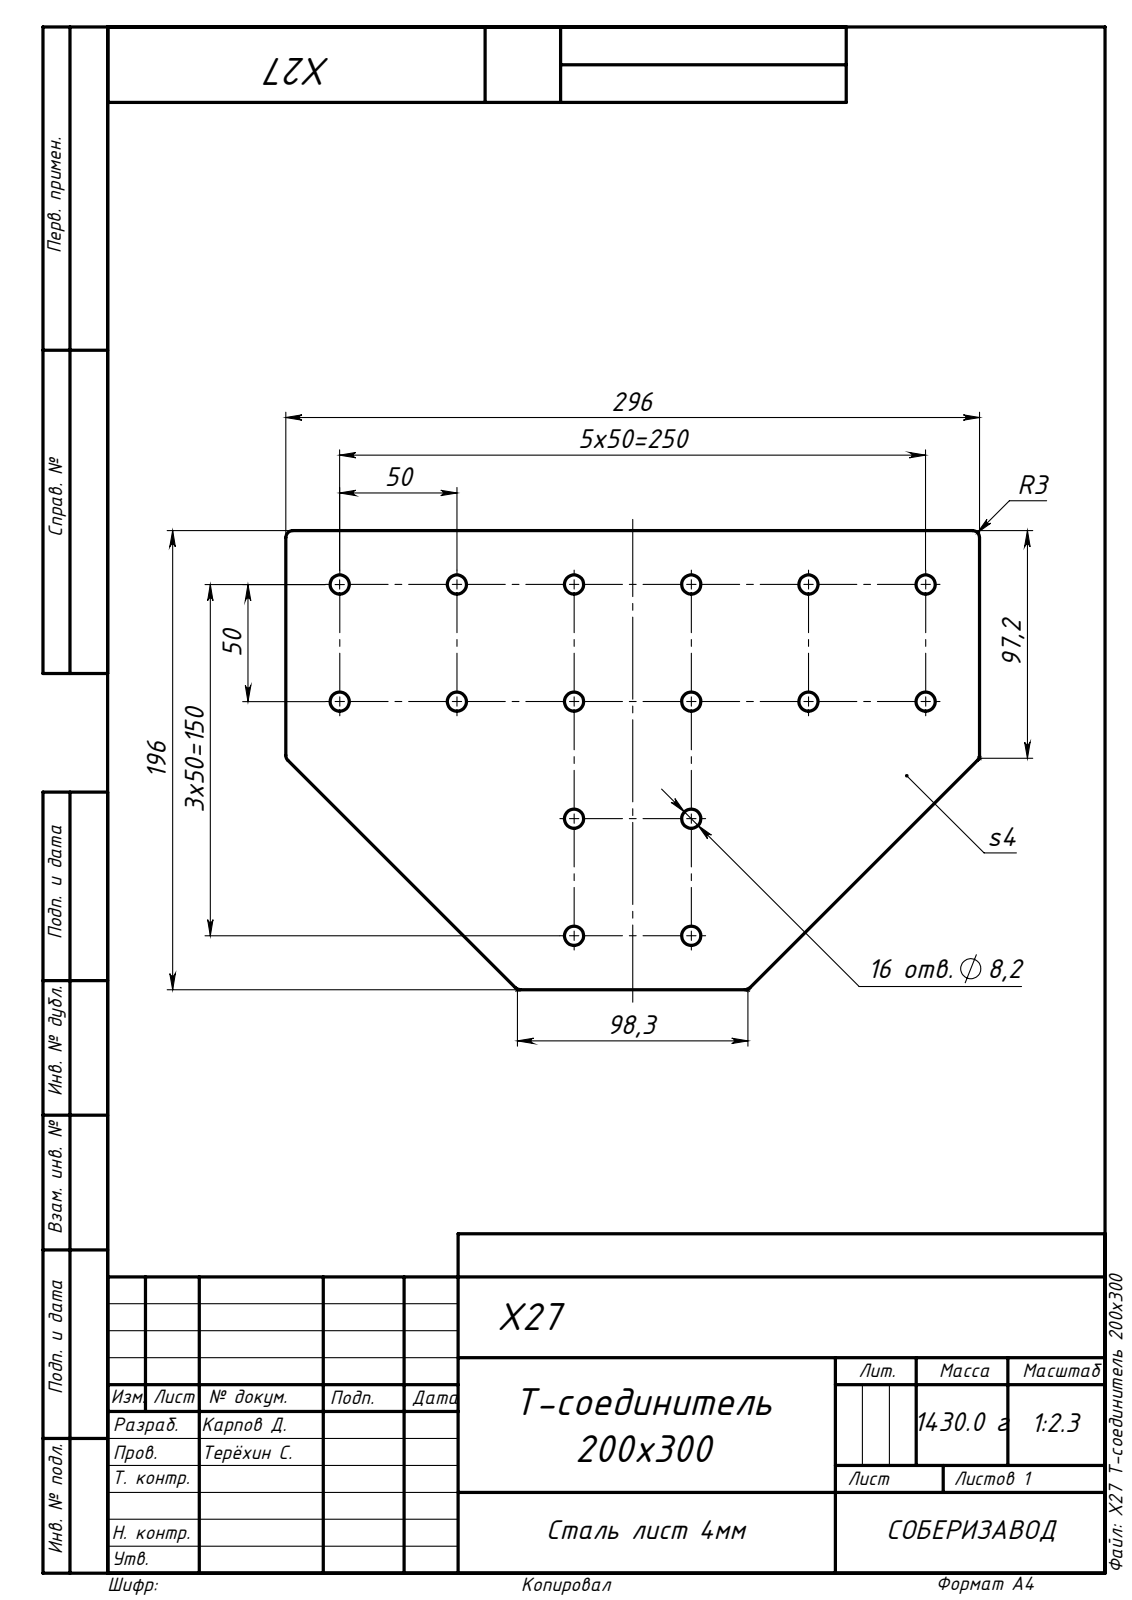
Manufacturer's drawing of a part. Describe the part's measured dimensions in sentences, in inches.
The part is named "X27 Т-соединитель 200х300". Its 3-D file was written by "SolidWorks 2019 (AUTOMOTIVE_DESIGN)". It is 1 solid with 46 faces: 8 planar, 38 cylindrical and 0 other. Overall it measures 11.654 by 7.717 by 0.157 inches. Its volume is 11.57 cubic inches and its surface area 154.9 square inches. Round holes: 16 of diameter 0.323. Partial cylindrical surfaces (rounded edges, fillets, slot ends): 6 of radius 0.118. The main face-to-face distances are 0.157, 7.717, 11.654. The hole center spacings are 1.969, 4.402, 2.784, 3.937, 6.225, 5.568, 5.906, 7.098.
